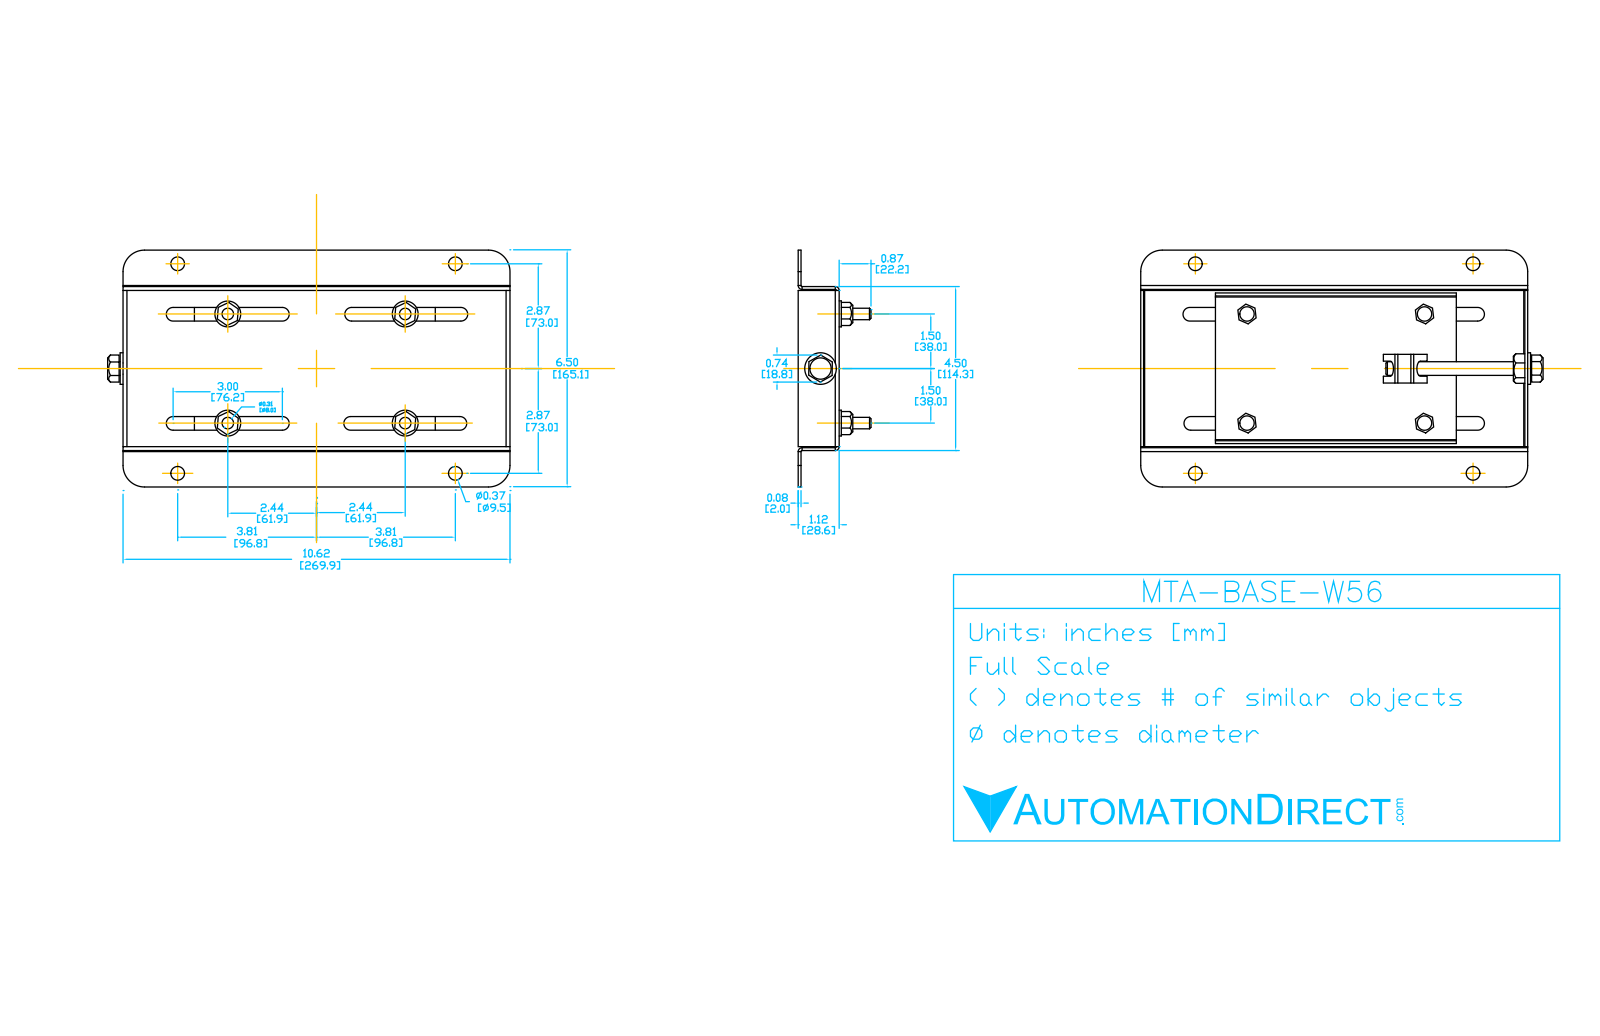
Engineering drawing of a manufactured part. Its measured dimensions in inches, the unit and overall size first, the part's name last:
Units: inches
Overall size (bounding box): 11.048 × 6.5 × 1.969
Round holes (diameter × count): ⌀0.315 ×4, ⌀0.354 ×4, ⌀0.375 ×3, ⌀0.375 ×2, ⌀0.472 ×1
Round bosses / shafts (diameter × count): ⌀0.709 ×4, ⌀0.866 ×1
Partial cylindrical surfaces — rounded edges, fillets, slot ends (radius × count): R0.029 ×10, R0.107 ×8, R0.187 ×8, R0.039 ×4, R0.591 ×4, R0.088 ×2, R0.207 ×2
Main face-to-face distances: 0.078, 1.047, 0.969, 0.156, 1.125, 0.891, 4.422, 4.5, 4.344, 10.547
Hole centre spacings: 3, 4.875, 5.724, 5.75, 7.625, 9.55, 1.909, 1.92
Volume: 11.59 in³ · Surface area: 292 in²
Bodies: 19 solids, 322 faces (165 planar, 103 cylindrical, 54 other)
Part name (STEP PRODUCT): W56
STEP written by: SolidWorks 2017 (AUTOMOTIVE_DESIGN)
